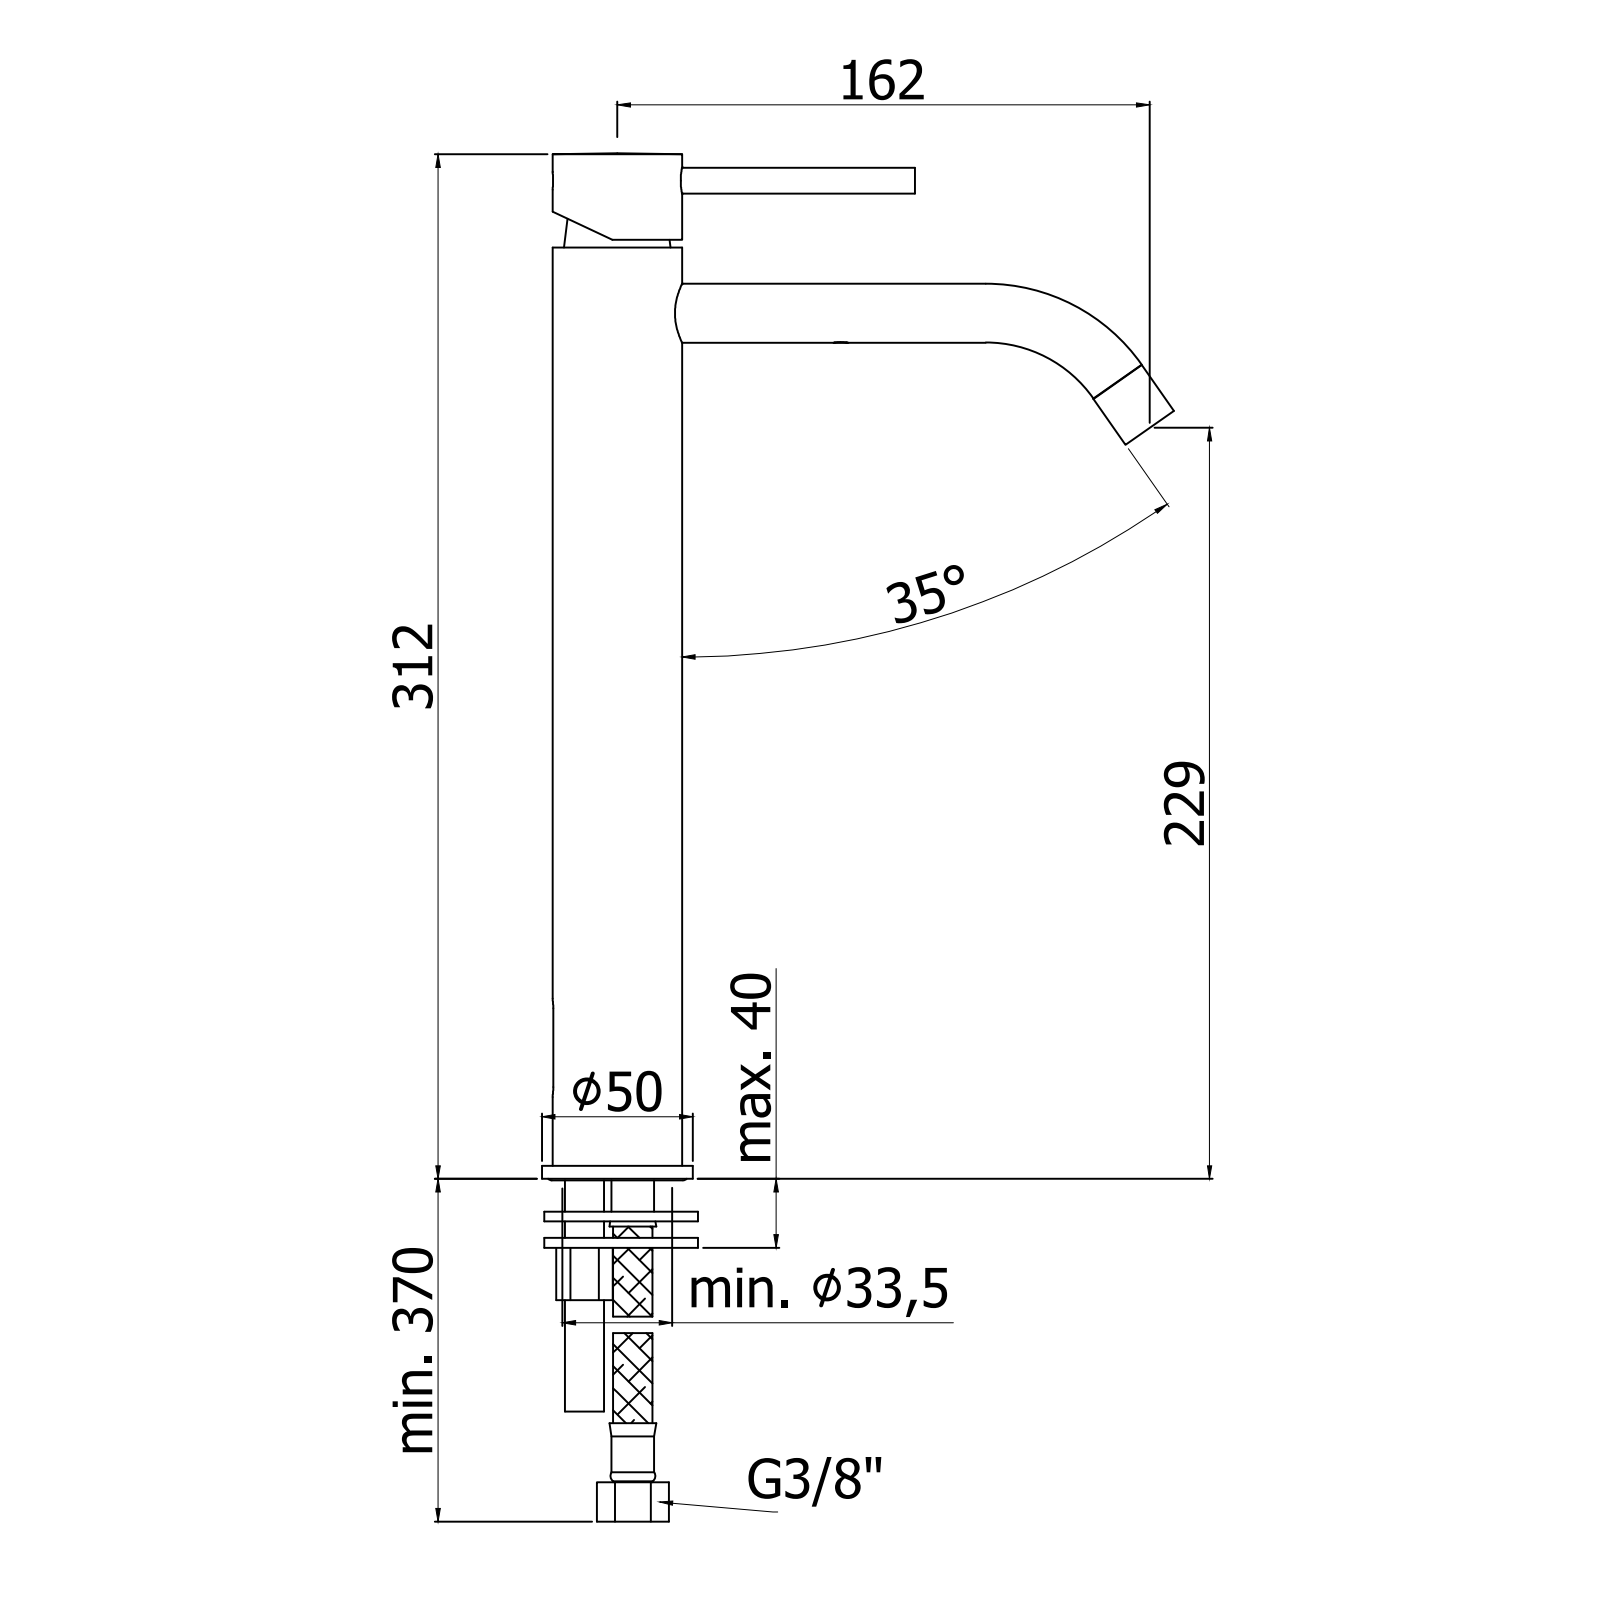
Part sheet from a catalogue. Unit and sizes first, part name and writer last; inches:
Units: inches
Overall size (bounding box): 12.289 × 7.699 × 1.969
Round holes (diameter × count): ⌀0.02 ×51, ⌀0.354 ×5, ⌀0.433 ×4, ⌀0.197 ×3, ⌀0.126 ×2, ⌀0.157 ×2, ⌀0.276 ×2, ⌀0.315 ×2, ⌀0.394 ×2, ⌀0.472 ×2, ⌀0.551 ×2, ⌀0.118 ×1
Round bosses / shafts (diameter × count): ⌀0.709 ×2, ⌀0.118 ×2, ⌀1.969 ×1, ⌀1.693 ×1, ⌀1.555 ×1, ⌀1.417 ×1, ⌀1.24 ×1, ⌀1.181 ×1
Partial cylindrical surfaces — rounded edges, fillets, slot ends (radius × count): R0.02 ×62, R0.012 ×34, R0.039 ×20, R0.118 ×12, R0.028 ×10, R0.01 ×8, R0.031 ×6, R0.138 ×5
Main face-to-face distances: 0.157, 0.079, 0.394, 0.551, 0.039, 10.079, 9.921, 0.118, 9.528, 0.709
Hole centre spacings: 0.132, 0.059, 0.187, 0.118, 0.083, 0.243, 0.167, 0.264
Volume: 19.31 in³ · Surface area: 190.7 in²
Bodies: 26 solids, 1654 faces (423 planar, 751 cylindrical, 480 other)
Part name (STEP PRODUCT): 1000489GR; 4071653_CORPO; 4071653_ROTAZIONE; 4071653_PERNO (+8 more)
STEP written by: CREO PARAMETRIC BY PTC INC, 2020044 (CONFIG_CONTROL_DESIGN)
